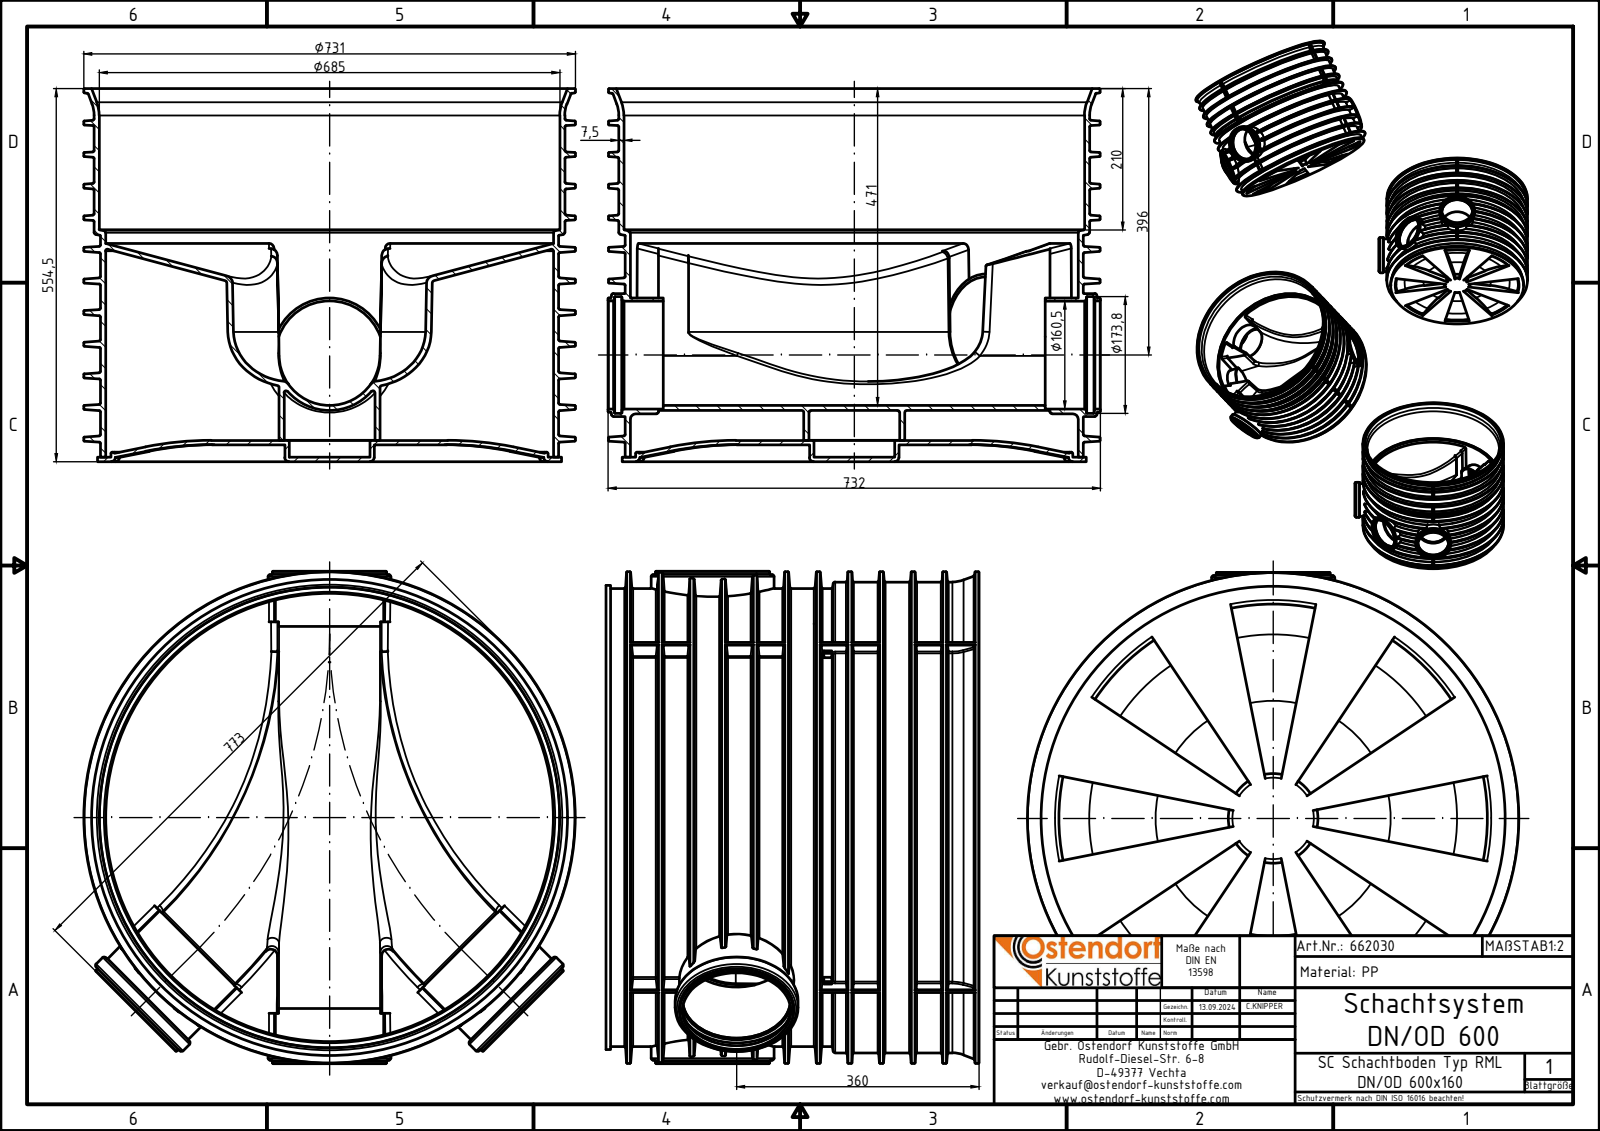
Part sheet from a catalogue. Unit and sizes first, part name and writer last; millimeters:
Units: millimetres
Overall size (bounding box): 732 × 731 × 554.5
Round holes (diameter × count): ⌀160.5 ×3, ⌀160.7 ×3, ⌀160.8 ×3, ⌀173.8 ×3, ⌀120 ×1, ⌀135 ×1, ⌀169.8 ×1, ⌀640 ×1, ⌀666 ×1, ⌀685 ×1
Round bosses / shafts (diameter × count): ⌀182.8 ×3, ⌀169.5 ×3, ⌀169.8 ×2, ⌀731 ×1, ⌀700 ×1, ⌀690 ×1, ⌀681 ×1, ⌀650 ×1
Partial cylindrical surfaces — rounded edges, fillets, slot ends (radius × count): R2 ×20, R1 ×8, R3 ×4, R75 ×3, R82.5 ×3, R66.5 ×1, R87.5 ×1, R318.5 ×1
Main face-to-face distances: 6.5, 25, 31.5, 18.5, 554.5, 548, 529.5, 523, 7.42, 7.58
Volume: 23 260 000 mm³ · Surface area: 5 631 000 mm²
Bodies: 2 solids, 1832 faces (180 planar, 300 cylindrical, 1352 other)
Part name (STEP PRODUCT): 662030z; 662030 Schacht DN600 Boden
STEP written by: Autodesk Inventor 2024 (AUTOMOTIVE_DESIGN)
